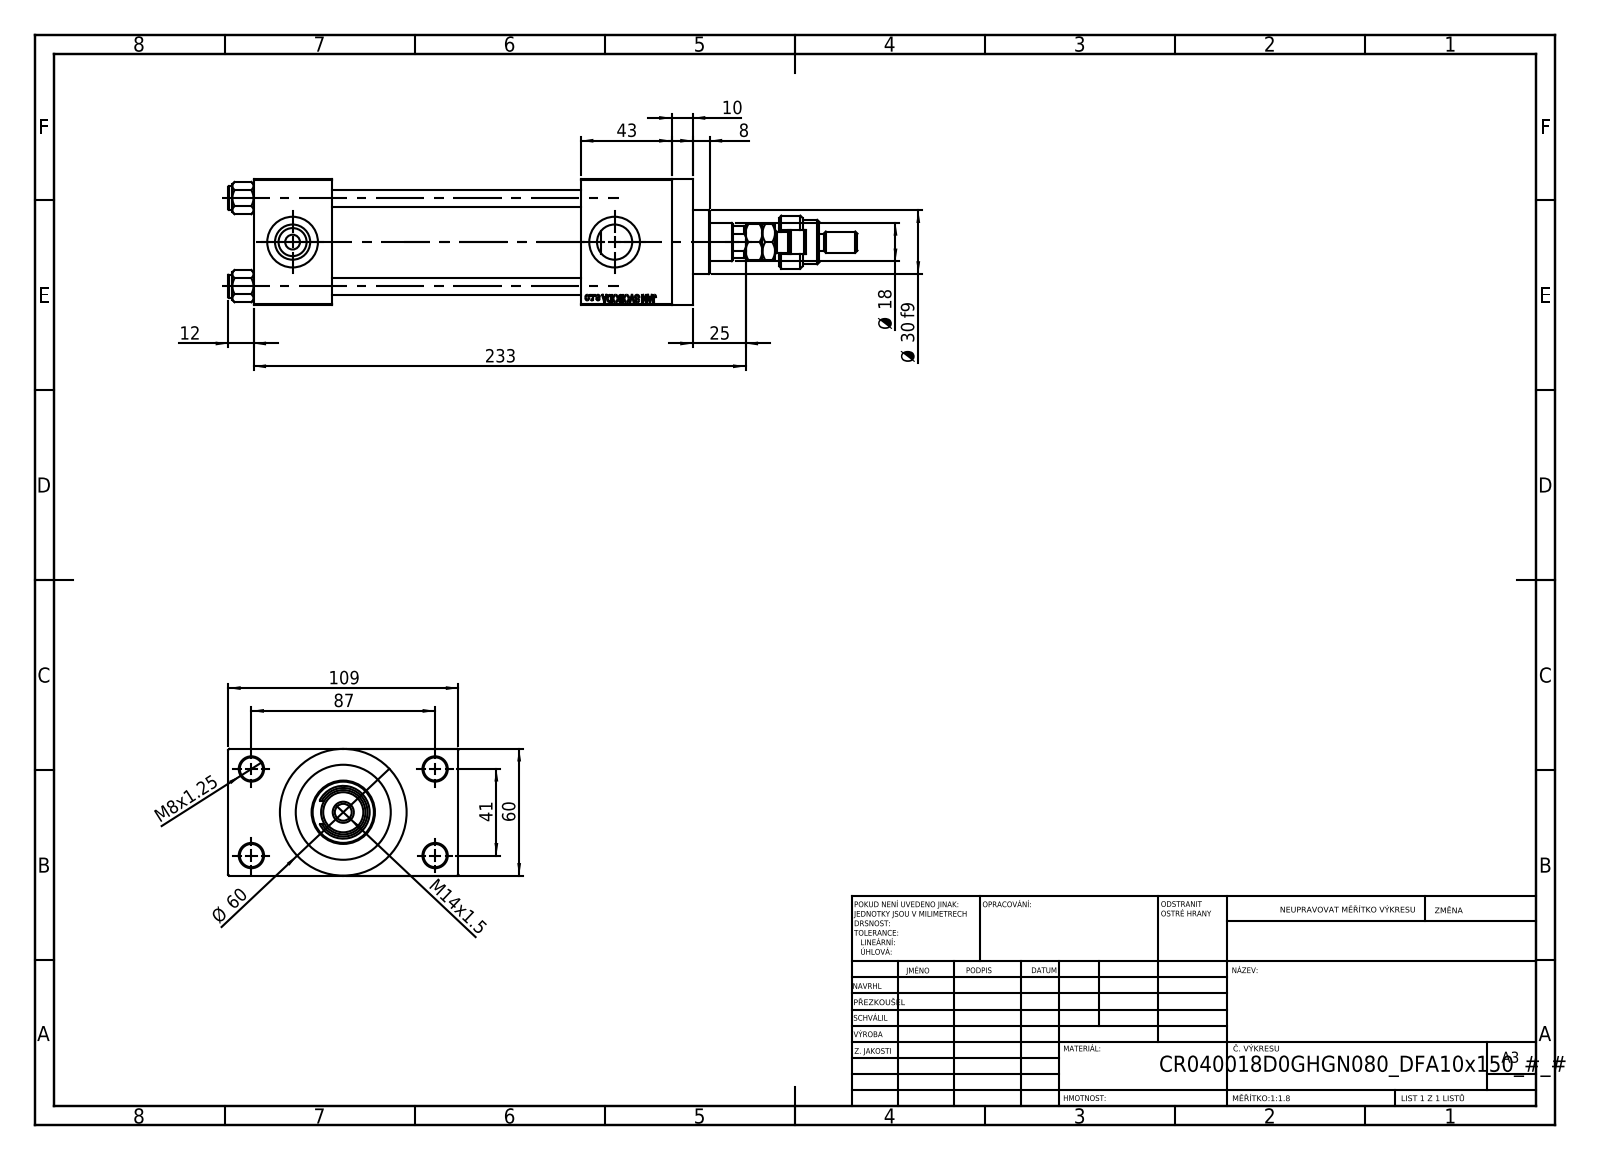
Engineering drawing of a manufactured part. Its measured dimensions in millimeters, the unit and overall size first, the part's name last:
Units: millimetres
Overall size (bounding box): 298 × 109 × 60
Round holes (diameter × count): ⌀8 ×4, ⌀11 ×4, ⌀7 ×2, ⌀16.66 ×2, ⌀24 ×2, ⌀8.5 ×1, ⌀18 ×1, ⌀21 ×1, ⌀31 ×1, ⌀40 ×1, ⌀45 ×1
Round bosses / shafts (diameter × count): ⌀11 ×4, ⌀60 ×1, ⌀46 ×1, ⌀30 ×1, ⌀25 ×1, ⌀16 ×1, ⌀10 ×1, ⌀8 ×1
Partial cylindrical surfaces — rounded edges, fillets, slot ends (radius × count): R5.5 ×1, R8.5 ×1, R8.75 ×1
Main face-to-face distances: 60, 24.5, 118, 84.5, 37, 155, 198, 161, 43, 53
Hole centre spacings: 22.65, 29.49, 41.7, 47.15, 48.09, 64.35, 76.49, 41
Volume: 575 965 mm³ · Surface area: 153 627 mm²
Bodies: 13 solids, 1189 faces (526 planar, 101 cylindrical, 562 other)
Part name (STEP PRODUCT): NUT_M5_D; FEMALE_PART_FOR_DFA; V215_VC_A; V215CR_D_Body (+3 more)
STEP written by: SolidWorks 2019 (CONFIG_CONTROL_DESIGN)
